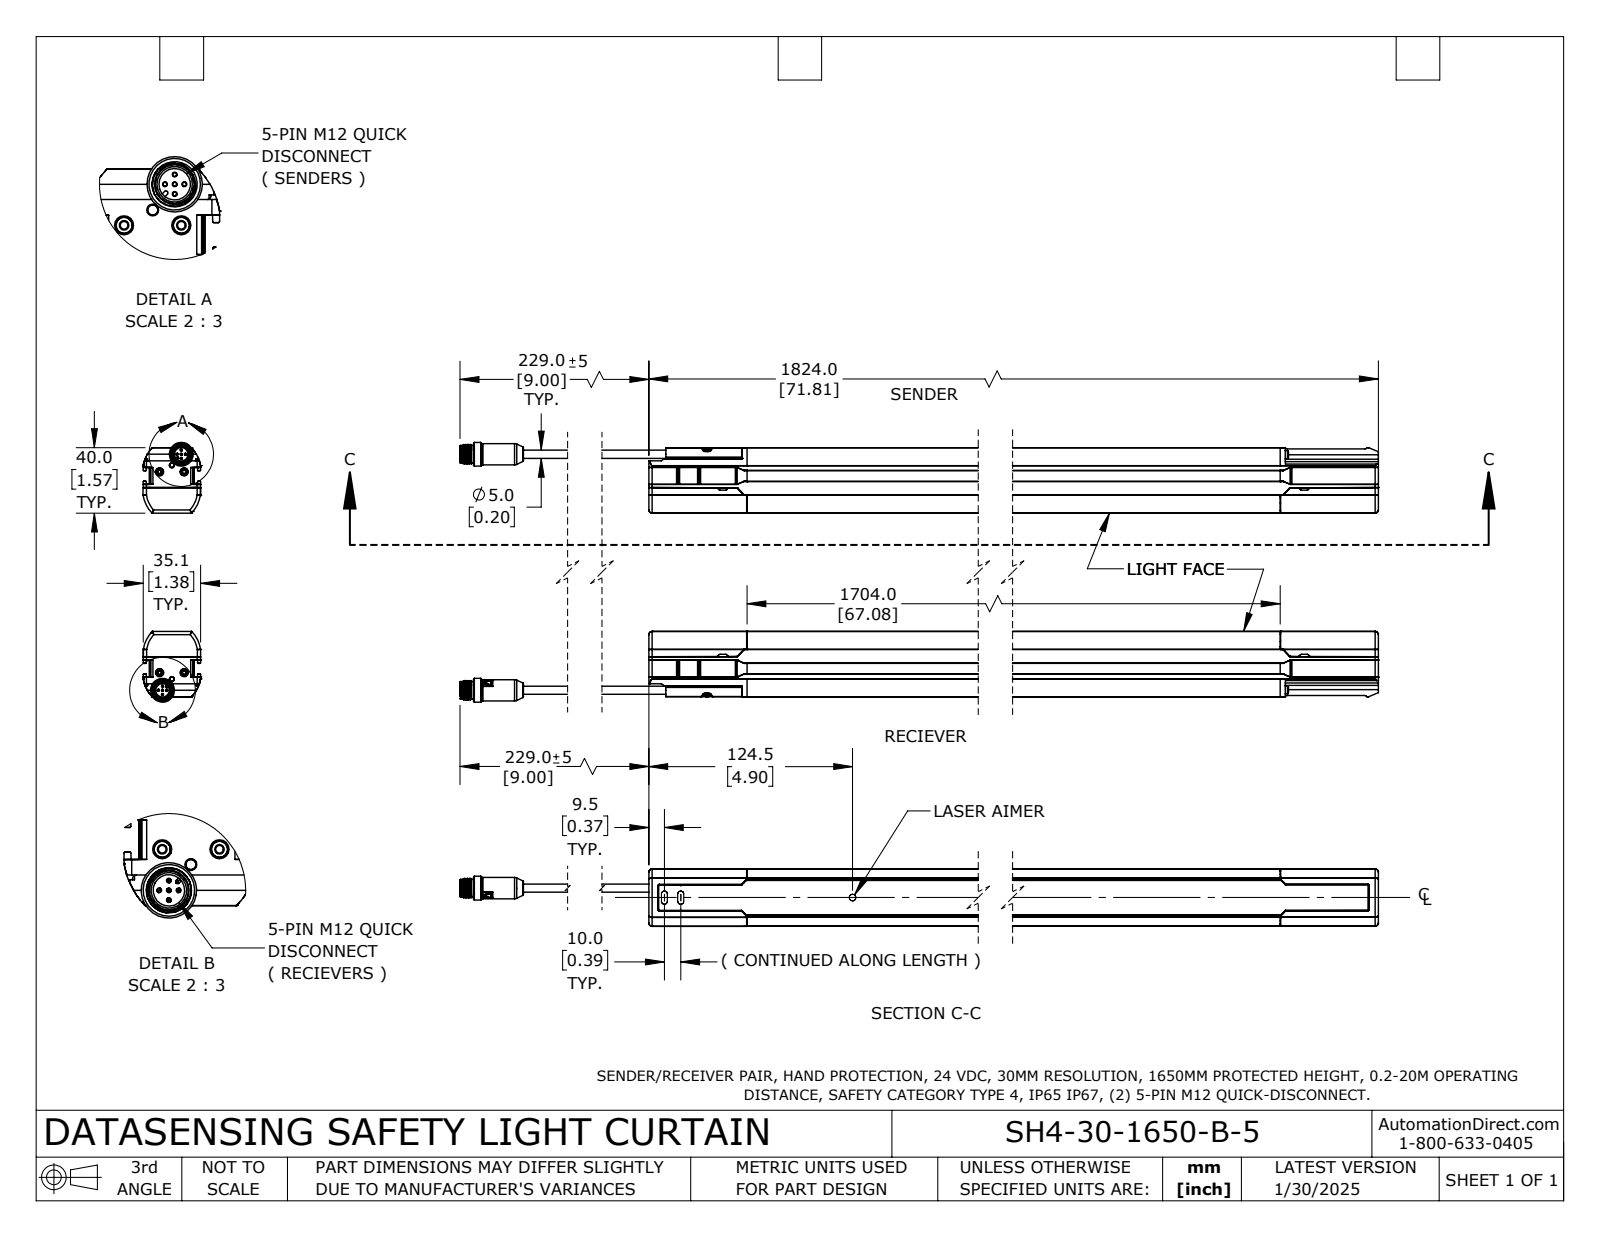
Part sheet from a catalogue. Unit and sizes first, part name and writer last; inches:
Units: inches
Overall size (bounding box): 74.303 × 6.248 × 1.384
Round holes (diameter × count): ⌀0.079 ×4, ⌀0.118 ×4, ⌀0.197 ×4, ⌀0.1 ×2, ⌀0.1 ×2, ⌀0.1 ×2, ⌀0.101 ×2, ⌀0.11 ×2, ⌀0.325 ×2, ⌀0.382 ×2, ⌀0.407 ×2, ⌀0.425 ×2
Round bosses / shafts (diameter × count): ⌀0.197 ×10, ⌀0.039 ×10, ⌀0.087 ×8, ⌀0.172 ×4, ⌀0.571 ×2, ⌀0.512 ×2, ⌀0.417 ×2, ⌀0.374 ×2
Partial cylindrical surfaces — rounded edges, fillets, slot ends (radius × count): R0.01 ×164, R0.016 ×66, R0.02 ×50, R0.008 ×36, R0.031 ×20, R0.031 ×12, R0.079 ×12, R0.059 ×10
Main face-to-face distances: 1.496, 4.496, 0.156, 1.222, 3, 5.992, 1.378, 1.067, 4.634, 0.069
Hole centre spacings: 0.866, 5.11, 5.183, 0.429, 0.591, 0.672, 4.831, 4.867
Volume: 239.5 in³ · Surface area: 998.7 in²
Bodies: 4 solids, 2582 faces (1178 planar, 778 cylindrical, 626 other)
Part name (STEP PRODUCT): SH4-30-1650-B-5
STEP written by: SolidWorks 2024 (AUTOMOTIVE_DESIGN)
